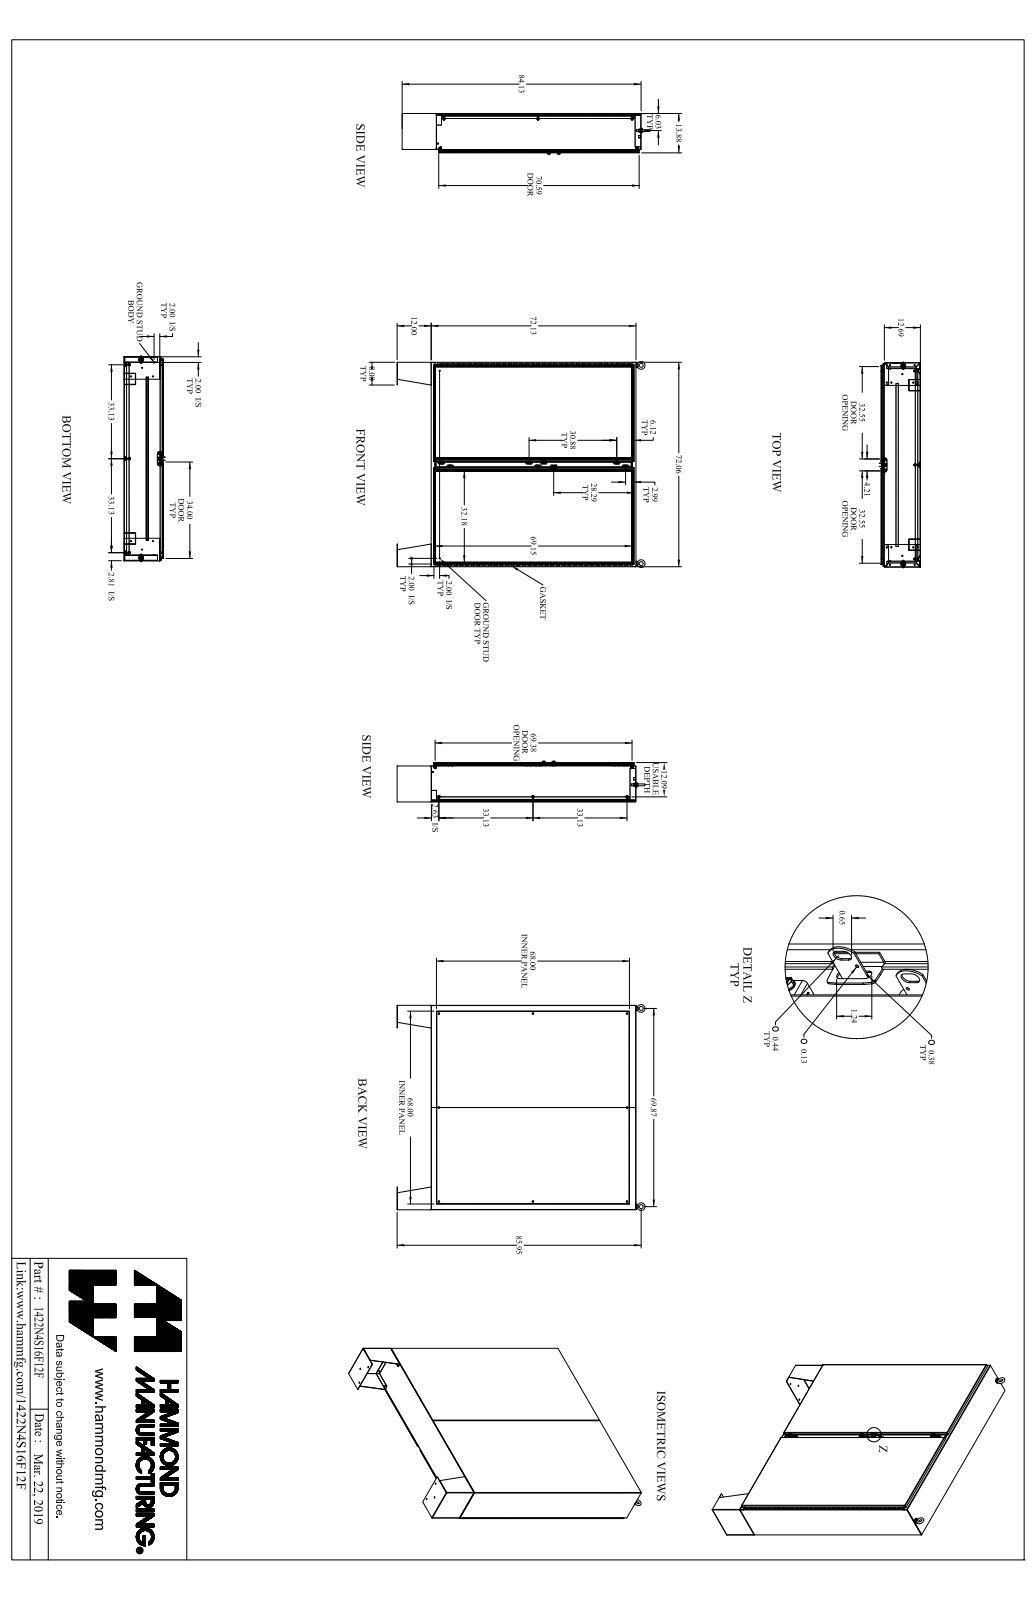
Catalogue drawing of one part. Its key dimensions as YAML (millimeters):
part_name: "1422N4S16F12F_Default"
step_written_by: "SolidWorks 2019 (CONFIG_CONTROL_DESIGN)"
units: millimeters
bodies: {solids: 110, faces: 3488, planar: 1684, cylindrical: 1584, other: 220}
overall_size: [2229.7, 1857.3, 366.7]
volume: 37180000
surface_area: 29510000
round_holes:
  - {diameter: 7.7, count: 24}
  - {diameter: 11.1, count: 14}
  - {diameter: 7.8, count: 8}
  - {diameter: 11.3, count: 8}
  - {diameter: 14.3, count: 8}
  - {diameter: 5.4, count: 6}
  - {diameter: 6.7, count: 6}
  - {diameter: 9.5, count: 6}
  - {diameter: 5.1, count: 3}
  - {diameter: 6.4, count: 3}
  - {diameter: 8, count: 3}
  - {diameter: 2.8, count: 2}
round_bosses_or_shafts:
  - {diameter: 25.4, count: 8}
  - {diameter: 16.5, count: 8}
  - {diameter: 9.5, count: 8}
  - {diameter: 8.4, count: 8}
  - {diameter: 12.7, count: 6}
  - {diameter: 9.9, count: 6}
  - {diameter: 6.2, count: 6}
  - {diameter: 8, count: 4}
partial_cylinders:
  - {radius: 1.2, count: 69}
  - {radius: 3.6, count: 69}
  - {radius: 6.4, count: 34}
  - {radius: 1.5, count: 18}
  - {radius: 2.9, count: 12}
  - {radius: 3.6, count: 12}
  - {radius: 3.2, count: 10}
  - {radius: 4.7, count: 10}
face_to_face_distances: [2.4, 350, 347.6, 352.4, 3.2, 304.7, 307.2, 42.8, 45.3, 310.3]
hole_center_spacings: [152.4, 1789.2, 304.8, 1808.5, 457.2, 609.6, 1884, 762]
